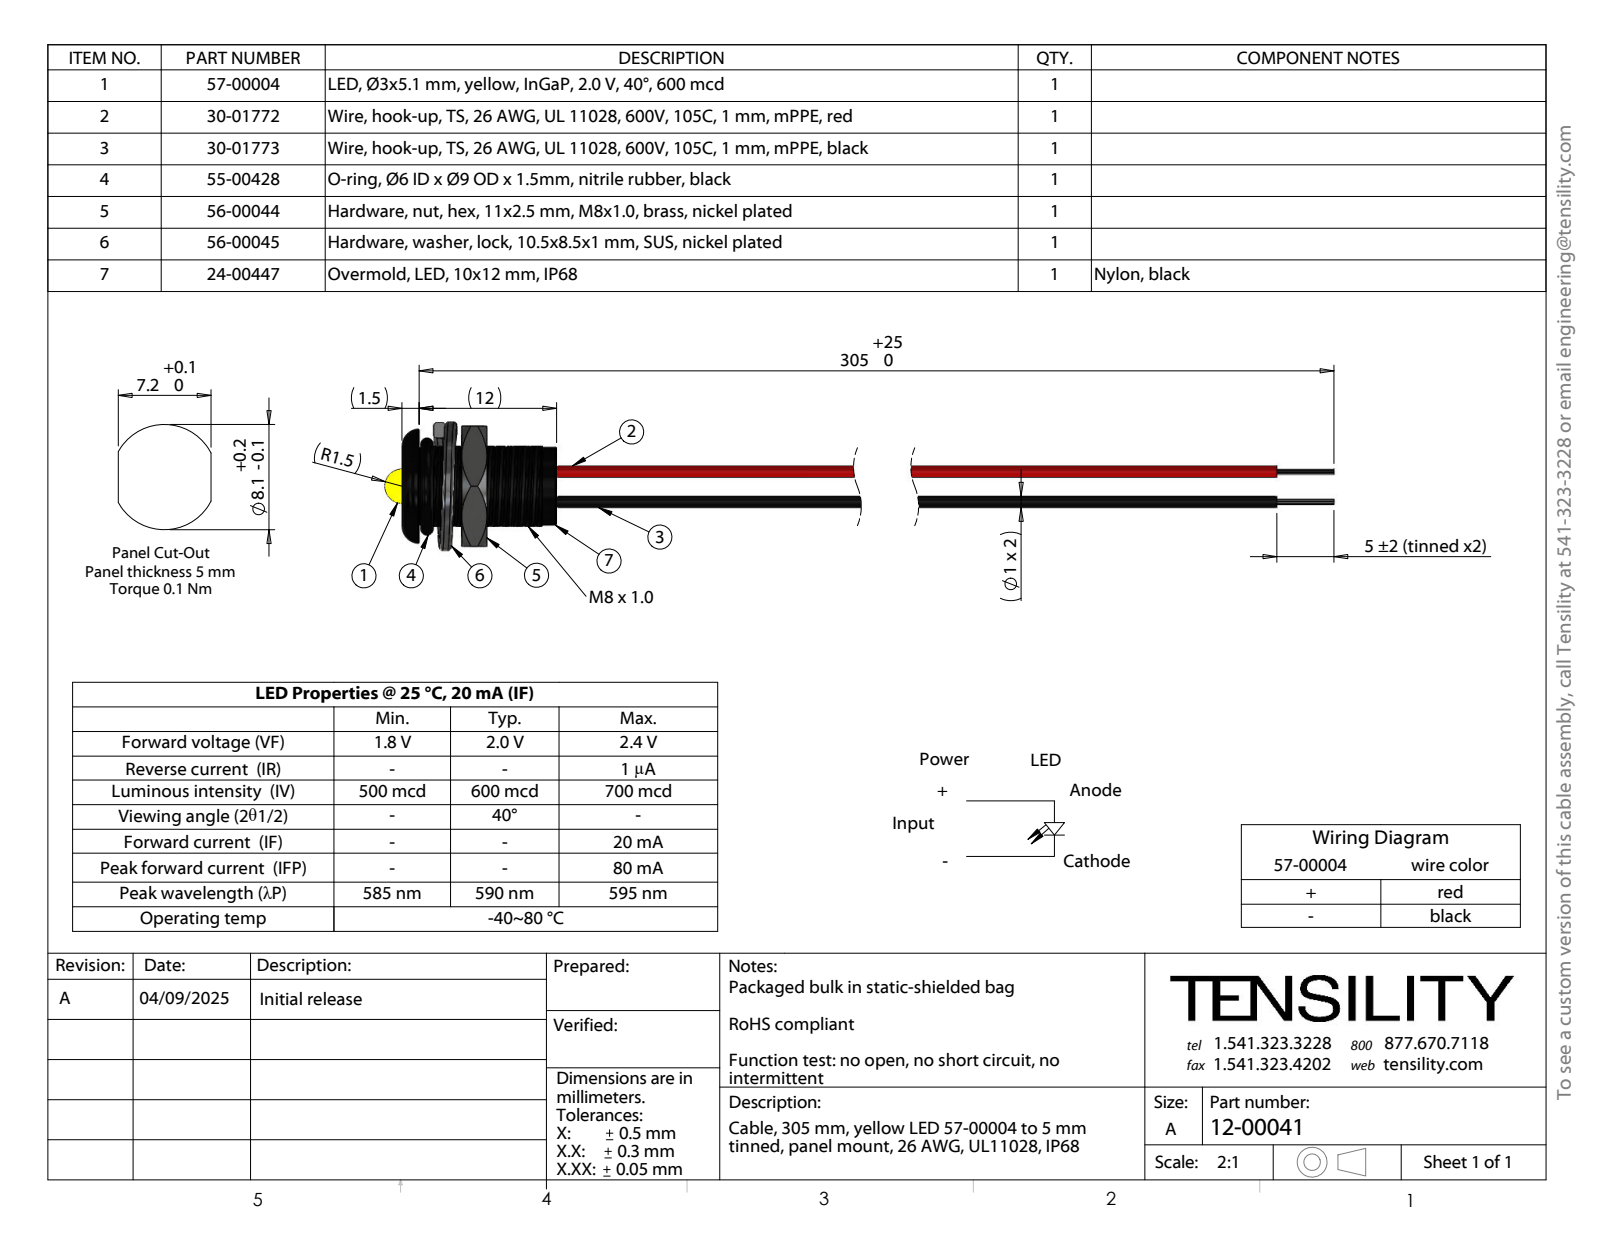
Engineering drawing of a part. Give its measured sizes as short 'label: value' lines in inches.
name: 57-00004_trimmed leads; 12-00041; 56-00044; 56-00045_Split washer (+4 more)
written by: SolidWorks 2021 (CONFIG_CONTROL_DESIGN)
unit: in
bodies: 57 solids, 555 faces (186 planar, 246 cylindrical, 123 other)
size: 6.693 × 0.477 × 0.441
volume: 0.061 in³; area: 9.157 in²
holes: 2× ⌀0.039
bosses: 2× ⌀0.039, 2× ⌀0.02, 1× ⌀0.268, 1× ⌀0.118
rounds: 1× R0.137, 1× R0.157
face distances: 0.059, 0.531, 0.472, 0.413, 0.205, 0.146, 0.326, 0.292, 0.233, 0.087
hole spacings: 0.014, 0.015, 0.013, 0.098, 0.099, 0.096, 0.096, 0.101
